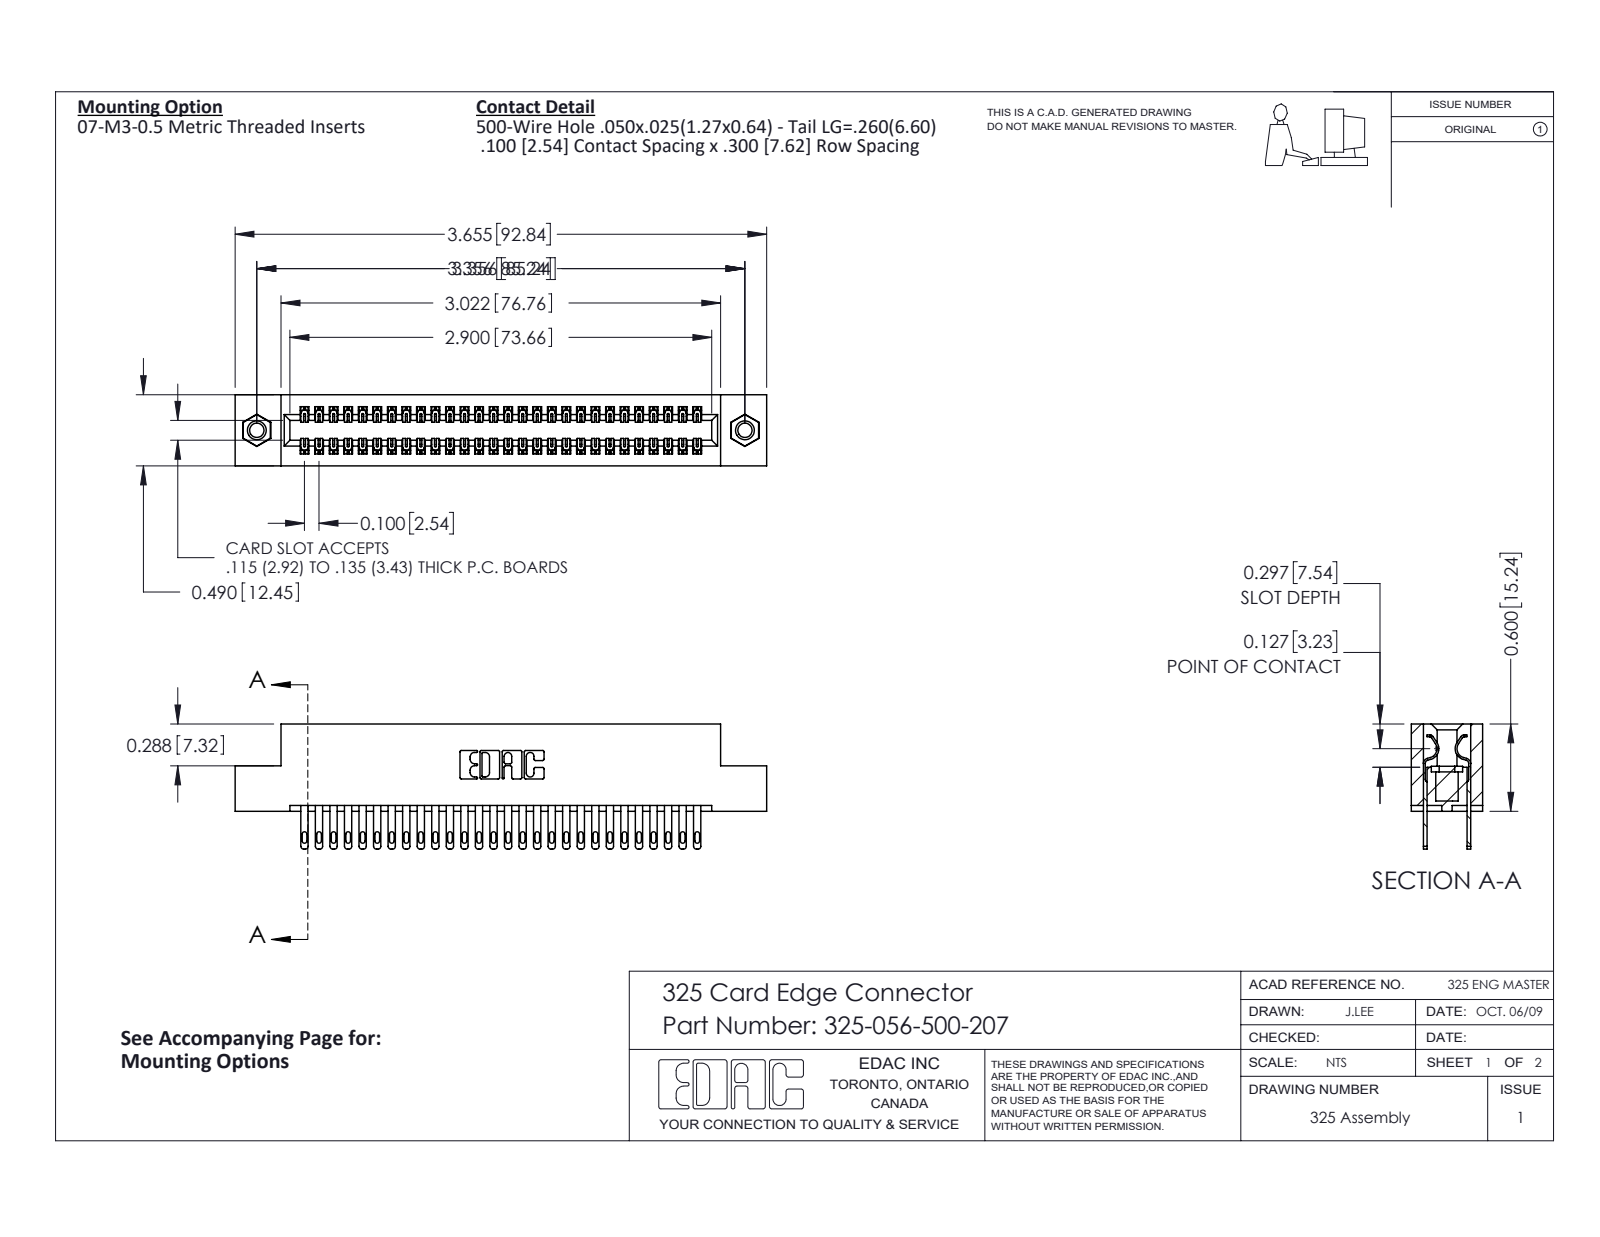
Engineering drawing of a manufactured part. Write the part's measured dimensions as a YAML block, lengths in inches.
part_name: "325 Part_TI; 325-292-001_325-293-100; 325-056-500-207; 345-250-001_345-250-005-103"
step_written_by: "SolidWorks 2016 (CONFIG_CONTROL_DESIGN)"
units: inches
bodies: {solids: 59, faces: 2862, planar: 1782, cylindrical: 1064, other: 16}
overall_size: [3.655, 0.86, 0.49]
volume: 0.733
surface_area: 22.98
round_holes:
  - {diameter: 0.098, count: 2}
  - {diameter: 0.125, count: 2}
  - {diameter: 0.16, count: 2}
round_bosses_or_shafts:
  - {diameter: 0.155, count: 2}
partial_cylinders:
  - {radius: 0.006, count: 84}
  - {radius: 0.016, count: 56}
  - {radius: 0.02, count: 56}
  - {radius: 0.01, count: 22}
  - {radius: 0.007, count: 6}
  - {radius: 0.031, count: 6}
  - {radius: 0.026, count: 3}
  - {radius: 0.014, count: 2}
face_to_face_distances: [0.083, 0.407, 0.3, 0.107, 0.383, 0.025, 0.49, 0.325, 0.275, 0.04]
hole_center_spacings: [3.356]
